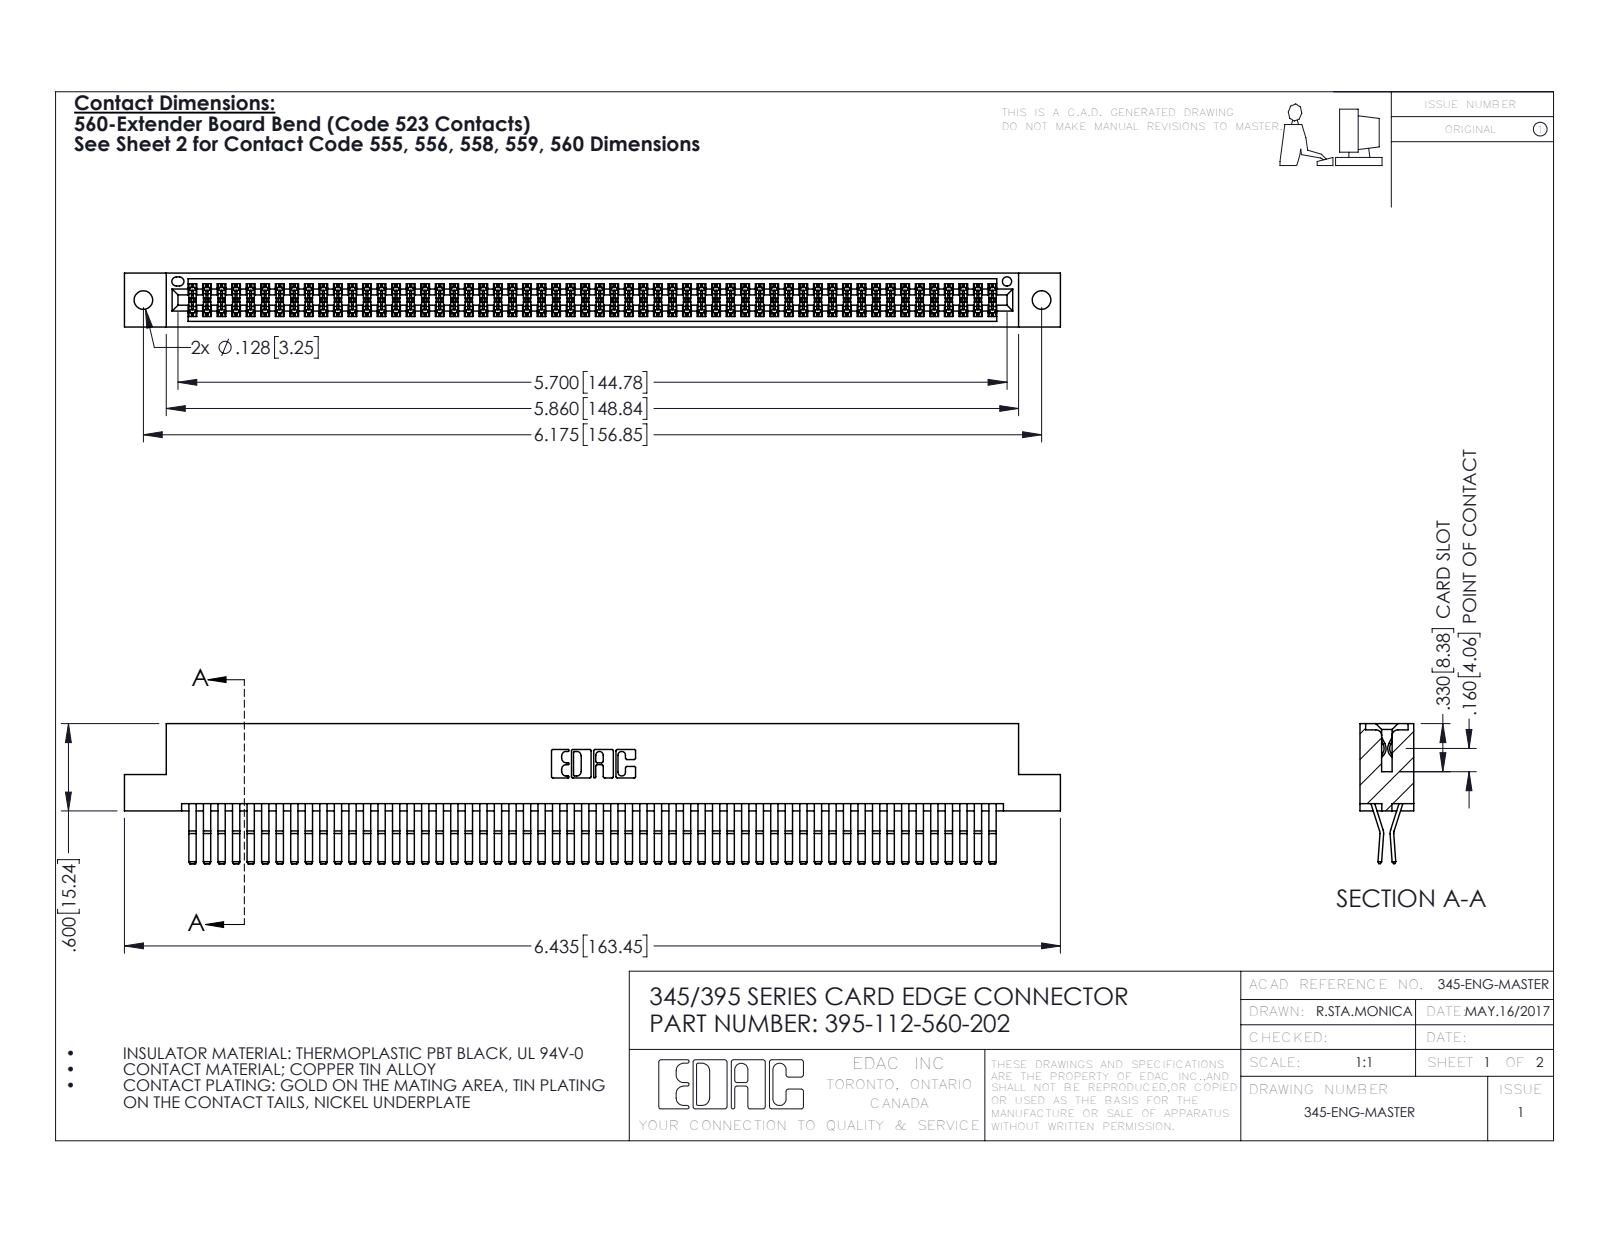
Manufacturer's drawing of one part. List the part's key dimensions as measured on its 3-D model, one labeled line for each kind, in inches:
Part name (STEP PRODUCT): 345-292-001_560 Tail; 345 Part_Flush Mounting Lugs - 0.128 Dia; 395-112-560-202
STEP written by: SolidWorks 2016 (CONFIG_CONTROL_DESIGN)
Units: inches
Bodies: 113 solids, 5950 faces (3776 planar, 2174 cylindrical, 0 other)
Overall size (bounding box): 6.435 × 0.962 × 0.37
Volume: 1.019 in³ · Surface area: 41.2 in²
Round holes (diameter × count): ⌀0.128 ×2, ⌀0.064 ×1
Partial cylindrical surfaces — rounded edges, fillets, slot ends (radius × count): R0.006 ×168, R0.01 ×22, R0.007 ×6, R0.031 ×6, R0.026 ×3, R0.01 ×2, R0.014 ×2, R0.019 ×2
Main face-to-face distances: 0.025, 0.298, 0.072, 0.37, 0.2, 0.098, 0.272, 0.225, 0.175, 0.149
Hole centre spacings: 0.27, 5.939, 6.175
